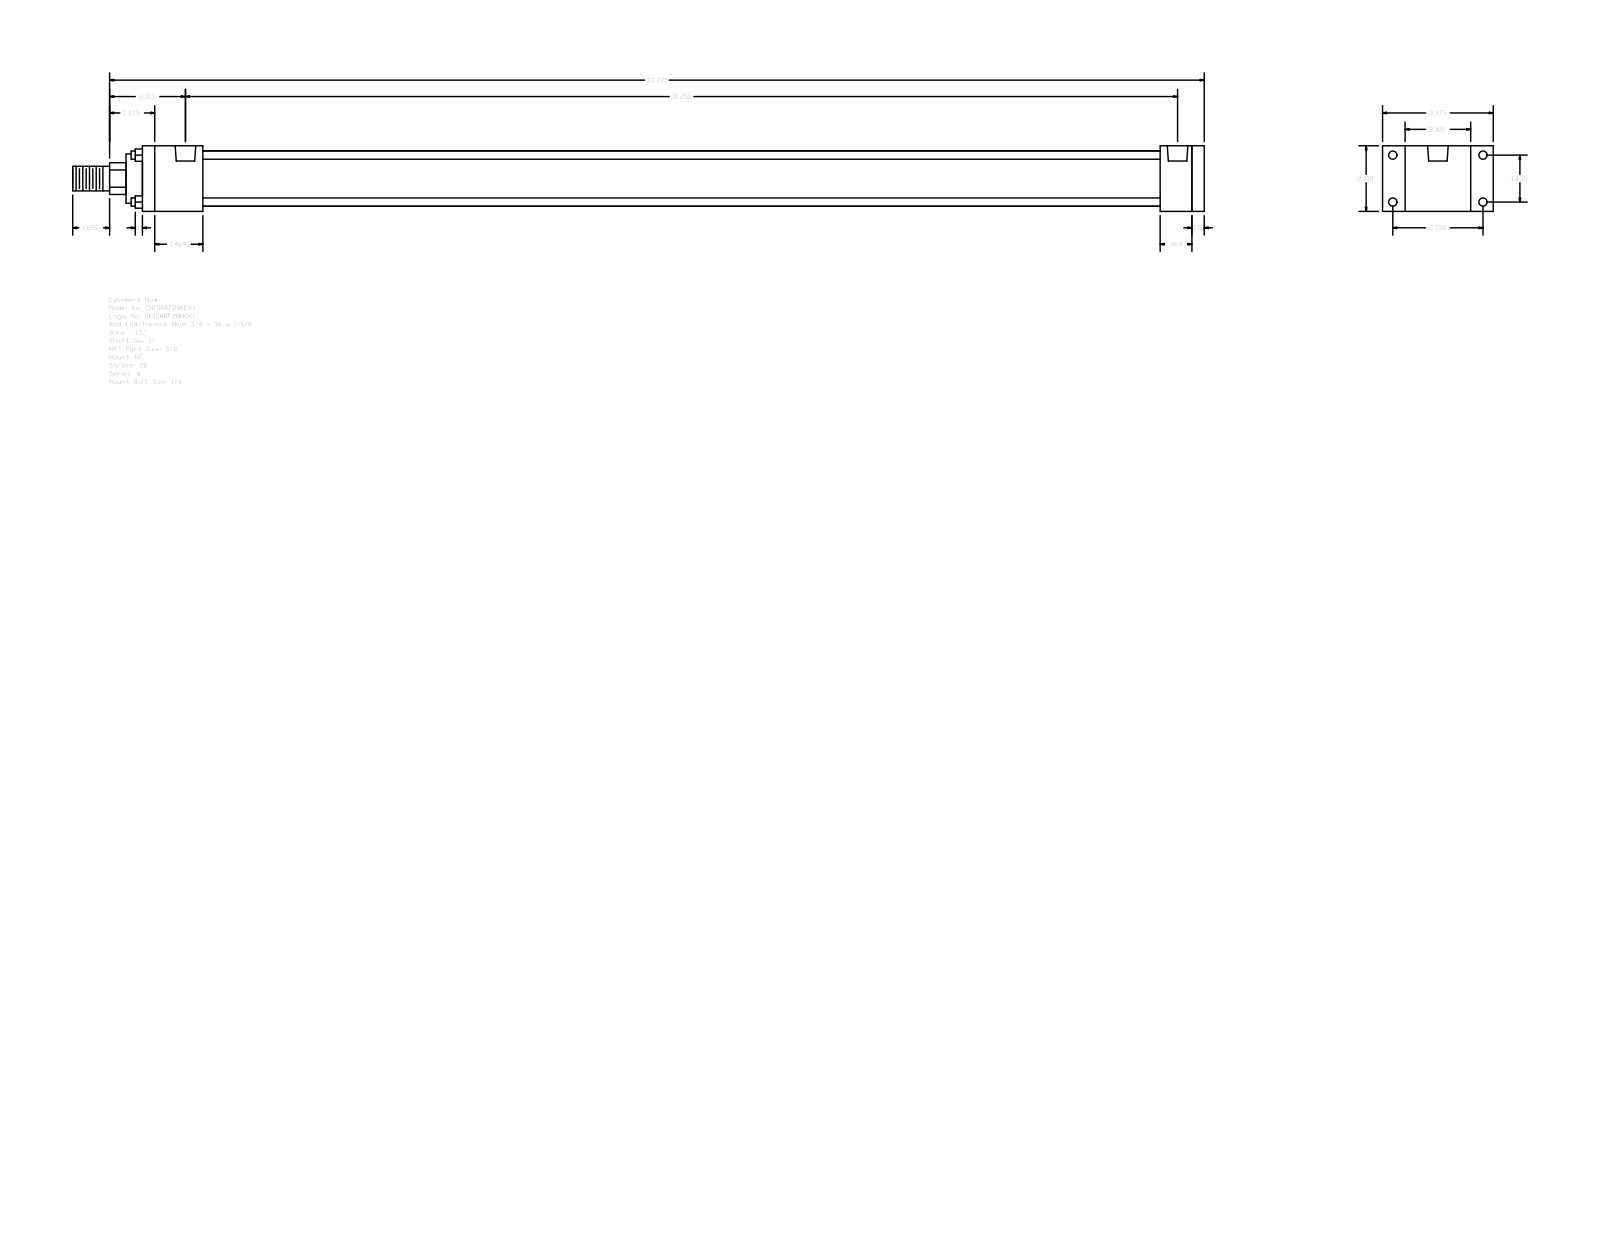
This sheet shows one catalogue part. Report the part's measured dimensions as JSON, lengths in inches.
{"part_name": "A_RF__0150_1", "step_written_by": "GSSL Pune (CONFIG_CONTROL_DESIGN)", "units": "inches", "bodies": {"solids": 0, "faces": 92, "planar": 64, "cylindrical": 28, "other": 0}, "overall_size": [34.5, 3.375, 2], "round_holes": [[0.219, 4], [0.25, 4], [0.627, 2]], "round_bosses_or_shafts": [[0.25, 4], [1.69, 1], [1.5, 1], [1, 1], [0.75, 1]], "partial_cylinders_radius": [[0.484, 1]], "face_to_face_distances": [2, 0.375, 32, 32.375, 31.031, 0.969, 1.344, 1.844, 29.187, 30.156], "hole_center_spacings": [0.156, 1.43, 2.75, 3.099, 29.937, 30.094, 30.25]}
